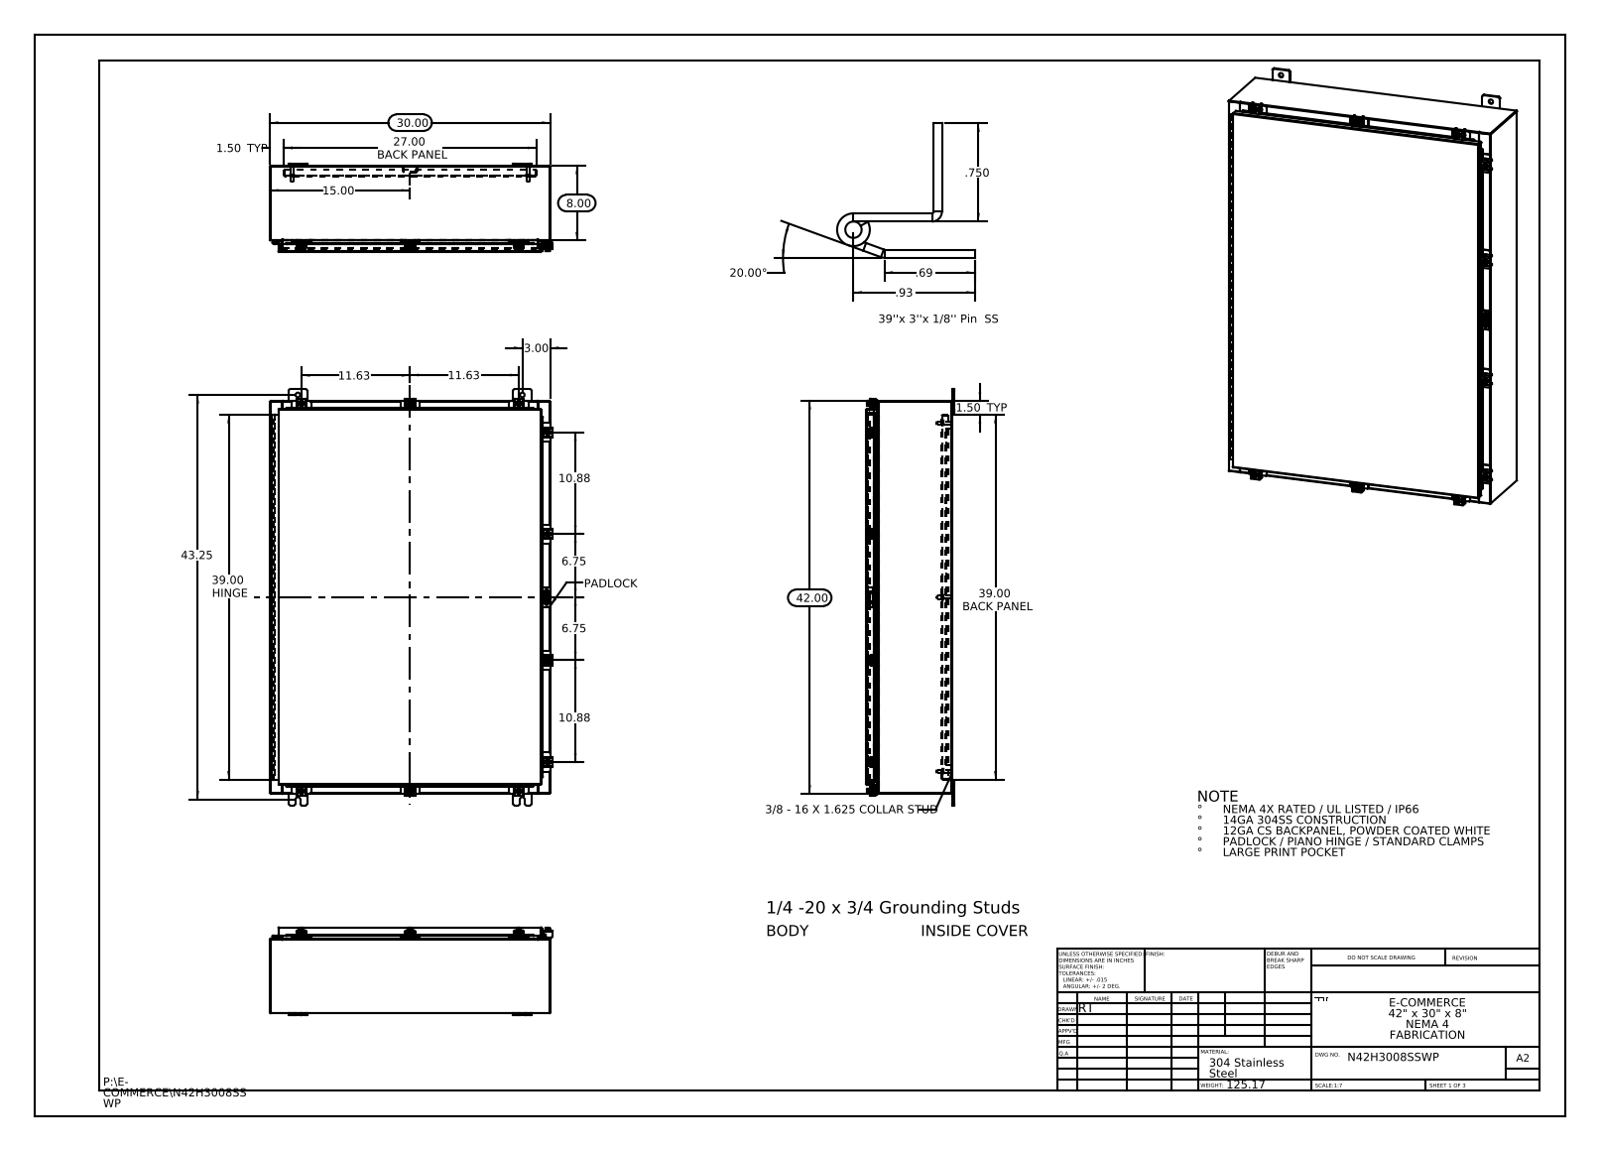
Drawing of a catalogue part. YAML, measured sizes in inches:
part_name: "N42H3008SSWP Padlock Staple; N42H3008SSWP; N42H3008SSWP Padlock Hasp; N42H3008SSWP Top (+8 more)"
step_written_by: "SolidWorks 2013 (CONFIG_CONTROL_DESIGN)"
units: inches
bodies: {solids: 70, faces: 2717, planar: 1420, cylindrical: 1149, other: 148}
overall_size: [44.5, 30.211, 9.389]
volume: 439.2
surface_area: 10915
round_holes:
  - {diameter: 0.213, count: 10}
  - {diameter: 0.26, count: 10}
  - {diameter: 0.5, count: 10}
  - {diameter: 0.125, count: 2}
  - {diameter: 0.125, count: 1}
round_bosses_or_shafts:
  - {diameter: 0.25, count: 11}
  - {diameter: 0.5, count: 10}
  - {diameter: 0.399, count: 10}
  - {diameter: 0.625, count: 6}
  - {diameter: 0.375, count: 6}
  - {diameter: 0.33, count: 6}
partial_cylinders:
  - {radius: 0.06, count: 46}
  - {radius: 0.013, count: 31}
  - {radius: 0.088, count: 25}
  - {radius: 0.19, count: 24}
  - {radius: 0.12, count: 20}
  - {radius: 0.141, count: 20}
  - {radius: 0.05, count: 15}
  - {radius: 0.08, count: 14}
face_to_face_distances: [0.075, 9.126, 9.051, 0.104, 9.201, 1, 8.126, 1.075, 8.051, 1.179]
hole_center_spacings: [2.326, 18.625, 20.75, 24.268, 31.376, 39.363, 41.326, 43.05]
